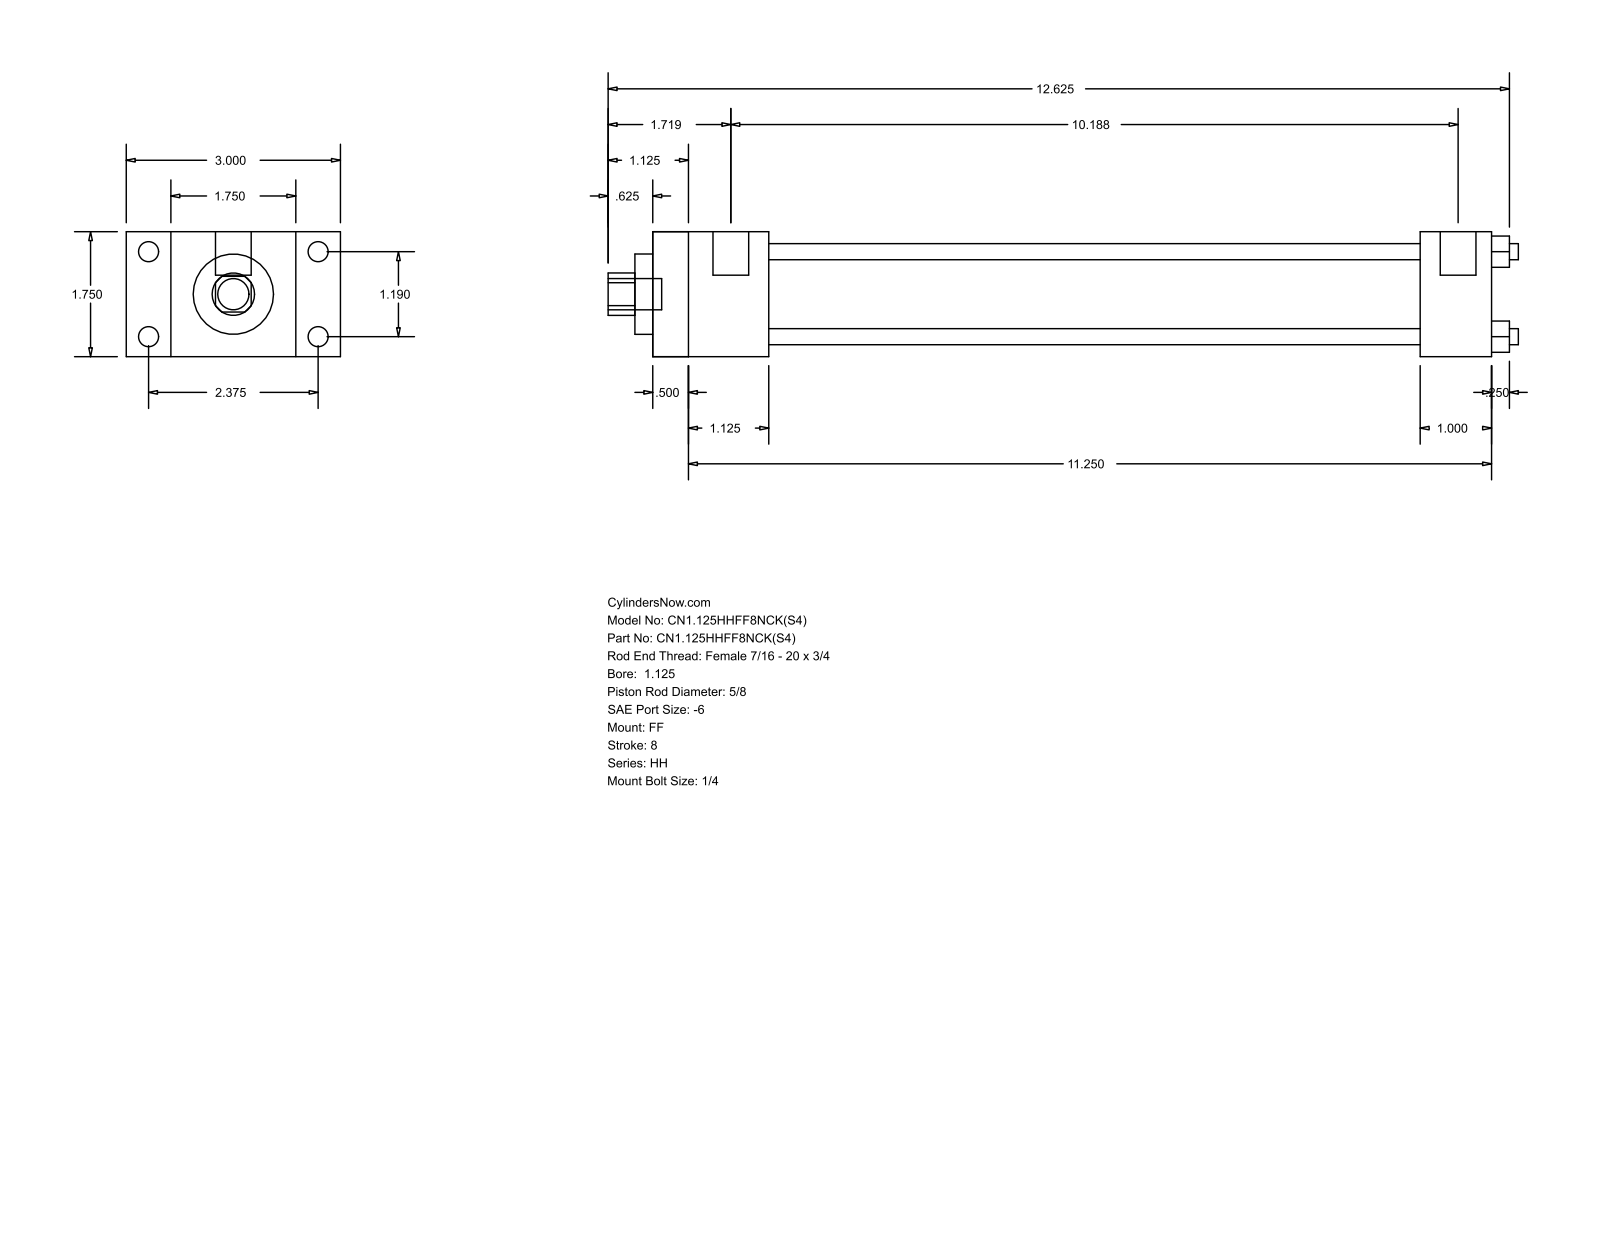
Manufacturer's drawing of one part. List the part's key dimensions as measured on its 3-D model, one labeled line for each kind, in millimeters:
Part name (STEP PRODUCT): HH_FF__0112_0.625
STEP written by: GSSL Pune (CONFIG_CONTROL_DESIGN)
Units: millimetres
Bodies: 0 solids, 92 faces (64 planar, 28 cylindrical, 0 other)
Overall size (bounding box): 323.85 × 76.2 × 44.45
Round holes (diameter × count): ⌀5.71 ×4, ⌀15.88 ×1, ⌀28.57 ×1, ⌀34.92 ×1
Round bosses / shafts (diameter × count): ⌀7.14 ×4, ⌀5.56 ×4, ⌀12.7 ×2, ⌀11.11 ×1
Partial cylindrical surfaces — rounded edges, fillets, slot ends (radius × count): R7.54 ×1
Main face-to-face distances: 44.46, 298.44, 15.87, 12.69, 285.75, 60.33, 28.58, 41.27, 273.05, 260.36
Hole centre spacings: 21.37, 30.22, 42.74
